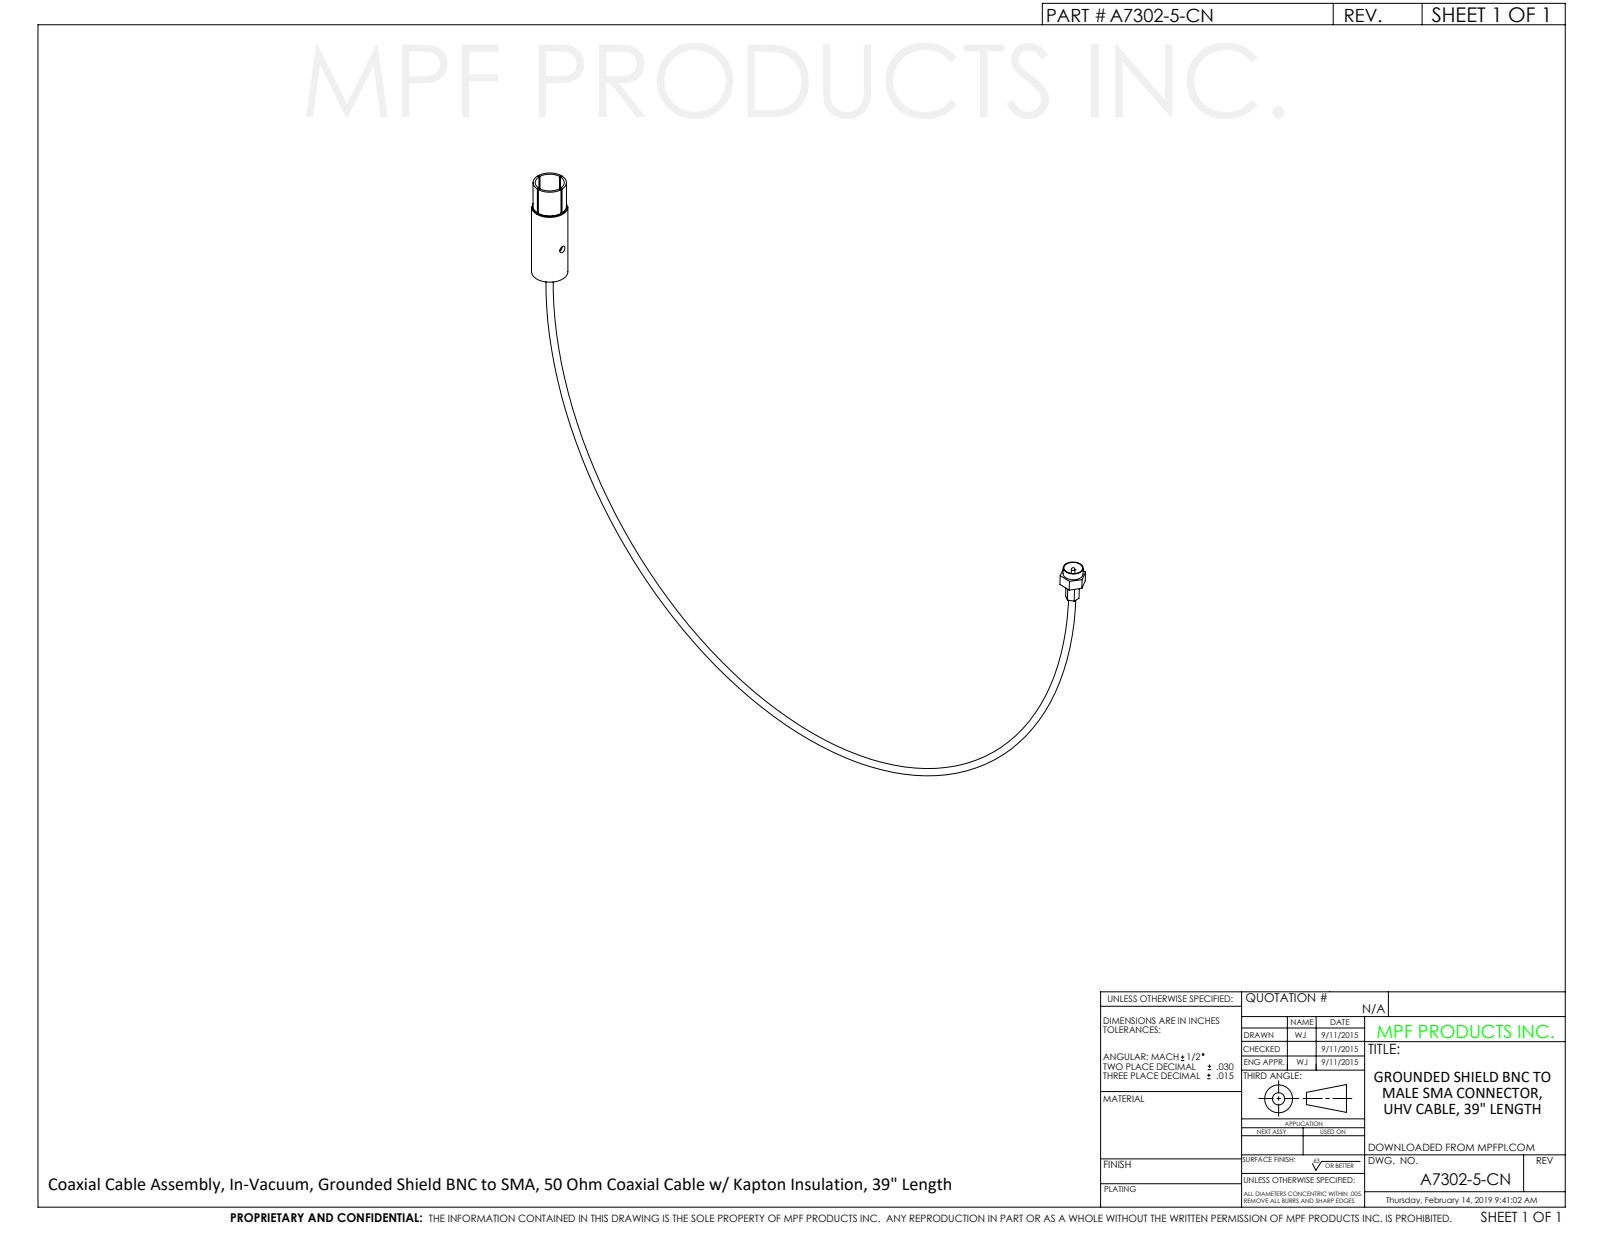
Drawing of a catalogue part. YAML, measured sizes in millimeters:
part_name: "A7302-5-CN"
step_written_by: "SolidWorks 2012 (CONFIG_CONTROL_DESIGN)"
units: millimeters
bodies: {solids: 1, faces: 58, planar: 33, cylindrical: 18, other: 7}
overall_size: [279, 173.6, 19.1]
volume: 11100
surface_area: 9432
round_holes:
  - {diameter: 2.5, count: 2}
  - {diameter: 12.7, count: 1}
  - {diameter: 15.5, count: 1}
round_bosses_or_shafts:
  - {diameter: 19.1, count: 1}
  - {diameter: 18, count: 1}
  - {diameter: 17, count: 1}
  - {diameter: 2.5, count: 1}
face_to_face_distances: [18.1, 7.6, 5.1, 38.1, 33, 0.5, 18.1, 2.5, 10.2, 4.2]
